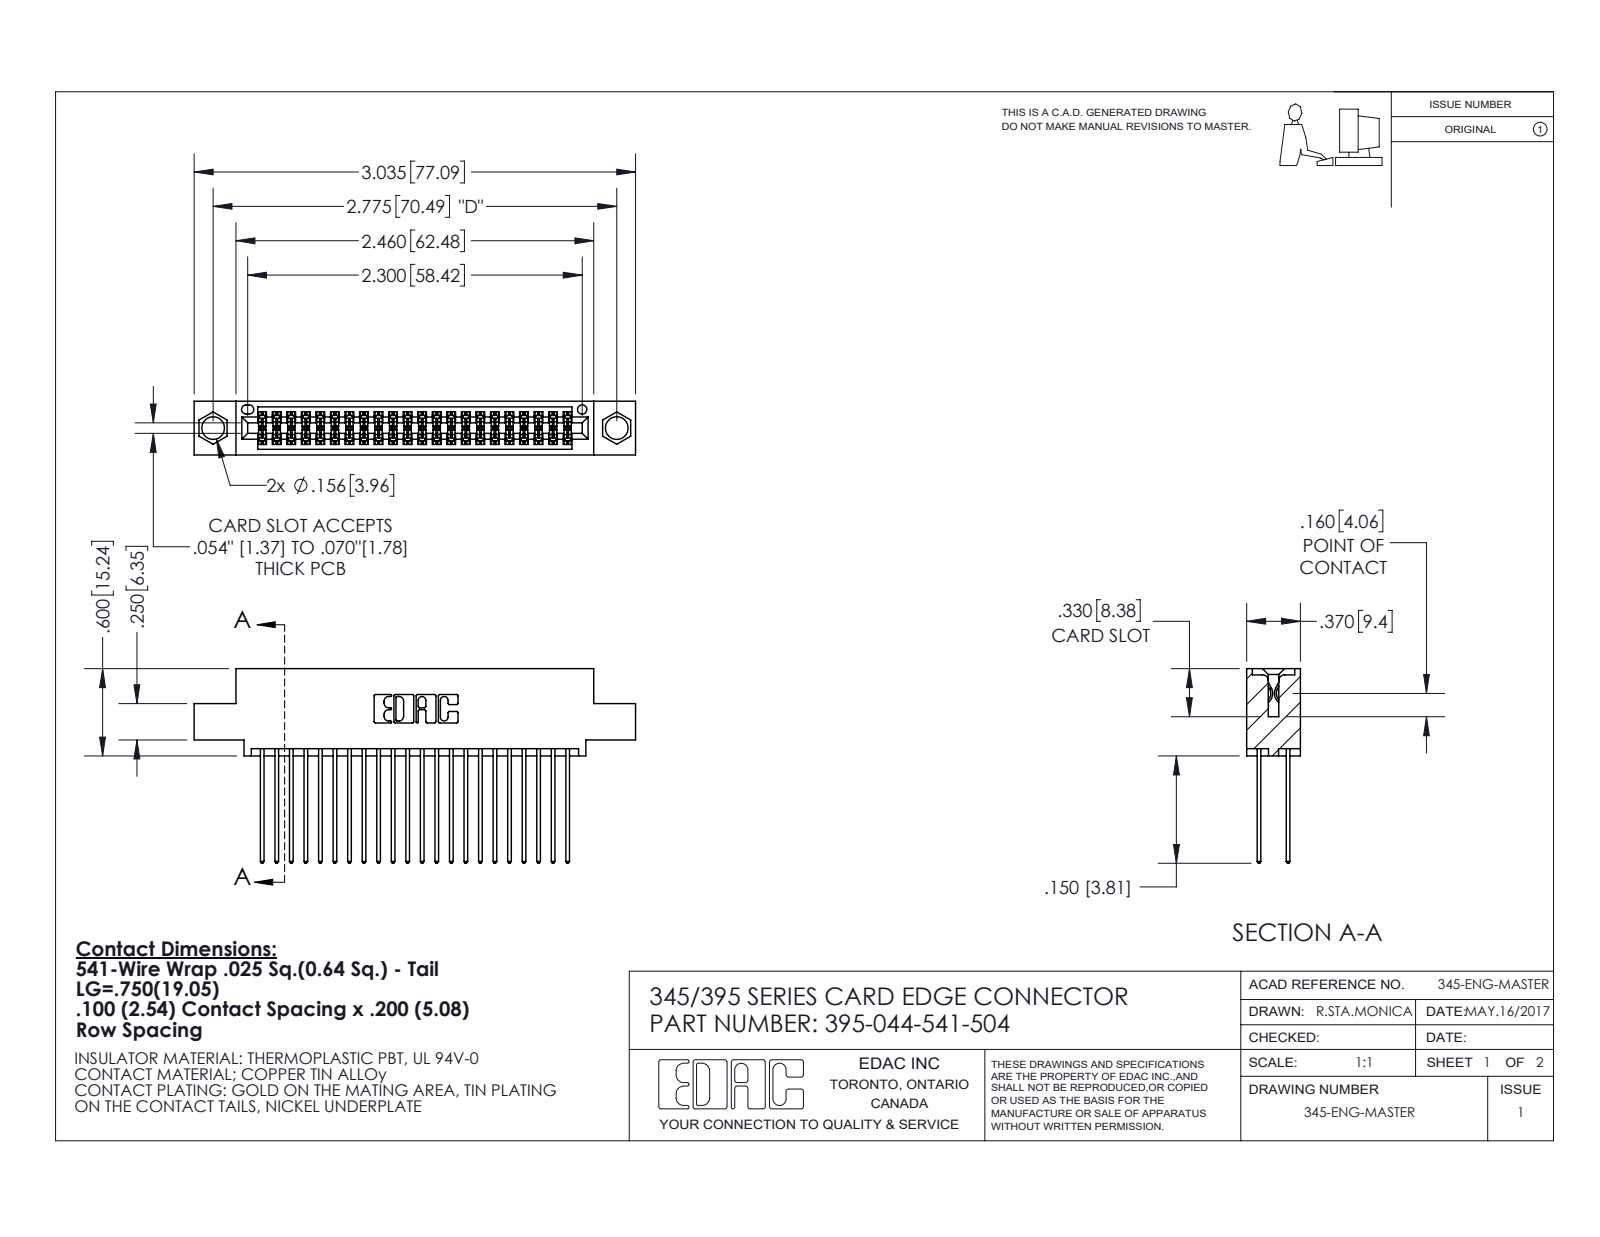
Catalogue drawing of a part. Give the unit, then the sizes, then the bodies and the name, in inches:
Units: inches
Overall size (bounding box): 3.035 × 1.337 × 0.37
Round holes (diameter × count): ⌀0.156 ×2, ⌀0.064 ×1
Partial cylindrical surfaces — rounded edges, fillets, slot ends (radius × count): R0.006 ×66, R0.01 ×44, R0.01 ×22, R0.007 ×6, R0.031 ×6, R0.026 ×3, R0.014 ×2, R0.019 ×2
Main face-to-face distances: 0.298, 0.072, 0.2, 0.098, 0.272, 0.025, 0.37, 0.225, 0.175, 0.149
Hole centre spacings: 0.27, 2.541, 2.775
Volume: 0.45 in³ · Surface area: 18.05 in²
Bodies: 45 solids, 2344 faces (1550 planar, 794 cylindrical, 0 other)
Part name (STEP PRODUCT): 345-292-001_345-293-141; 395-044-541-504; 345 Part_0.110 Offset - 0.156 Dia-TI
STEP written by: SolidWorks 2020 (CONFIG_CONTROL_DESIGN)
